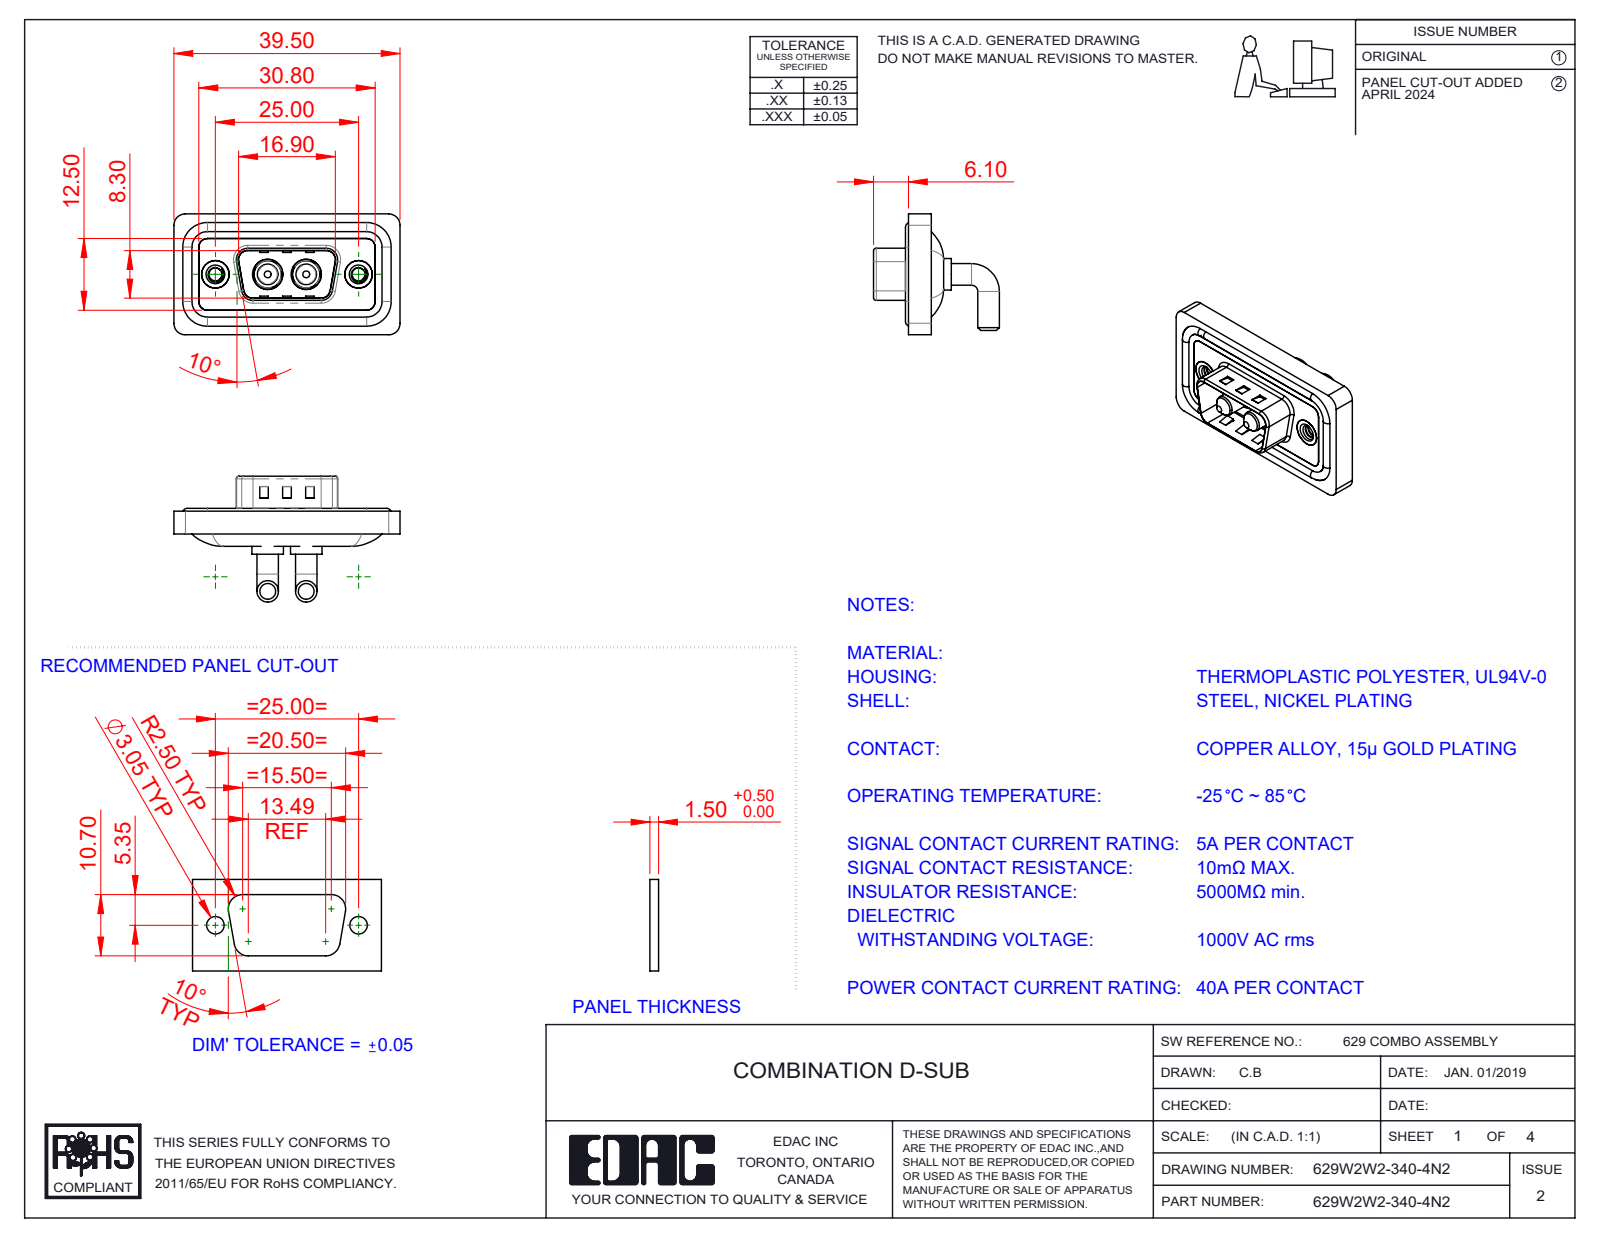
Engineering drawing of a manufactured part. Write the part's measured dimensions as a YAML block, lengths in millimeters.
part_name: "629Combo Threaded Rivet_2; 629Combo Shell Front_09 Contacts; 629Combo Housing_2W2; 629W2W2-340-4N2 (+3 more)"
step_written_by: "SolidWorks 2023 (CONFIG_CONTROL_DESIGN)"
units: millimeters
bodies: {solids: 11, faces: 497, planar: 165, cylindrical: 222, other: 110}
overall_size: [39.5, 21.98, 21.1]
volume: 4741
surface_area: 7255
round_holes:
  - {diameter: 2.26, count: 2}
  - {diameter: 4, count: 2}
  - {diameter: 4.8, count: 2}
  - {diameter: 4.85, count: 2}
  - {diameter: 5, count: 2}
  - {diameter: 5.3, count: 2}
round_bosses_or_shafts:
  - {diameter: 3.75, count: 4}
  - {diameter: 1.6, count: 4}
  - {diameter: 5.5, count: 2}
  - {diameter: 5.2, count: 2}
  - {diameter: 4.9, count: 2}
  - {diameter: 4.75, count: 2}
  - {diameter: 3.6, count: 2}
partial_cylinders:
  - {radius: 1.5, count: 18}
  - {radius: 2, count: 18}
  - {radius: 0.5, count: 8}
  - {radius: 1.6, count: 8}
  - {radius: 0.25, count: 4}
  - {radius: 0.6, count: 4}
  - {radius: 0.65, count: 4}
  - {radius: 0.9, count: 4}
face_to_face_distances: [0.4, 2.9, 1.1, 0.8, 2.1, 2.5, 3.1, 1.6, 4.5, 1.5]
hole_center_spacings: [9.14, 15.86, 6.72, 25]
